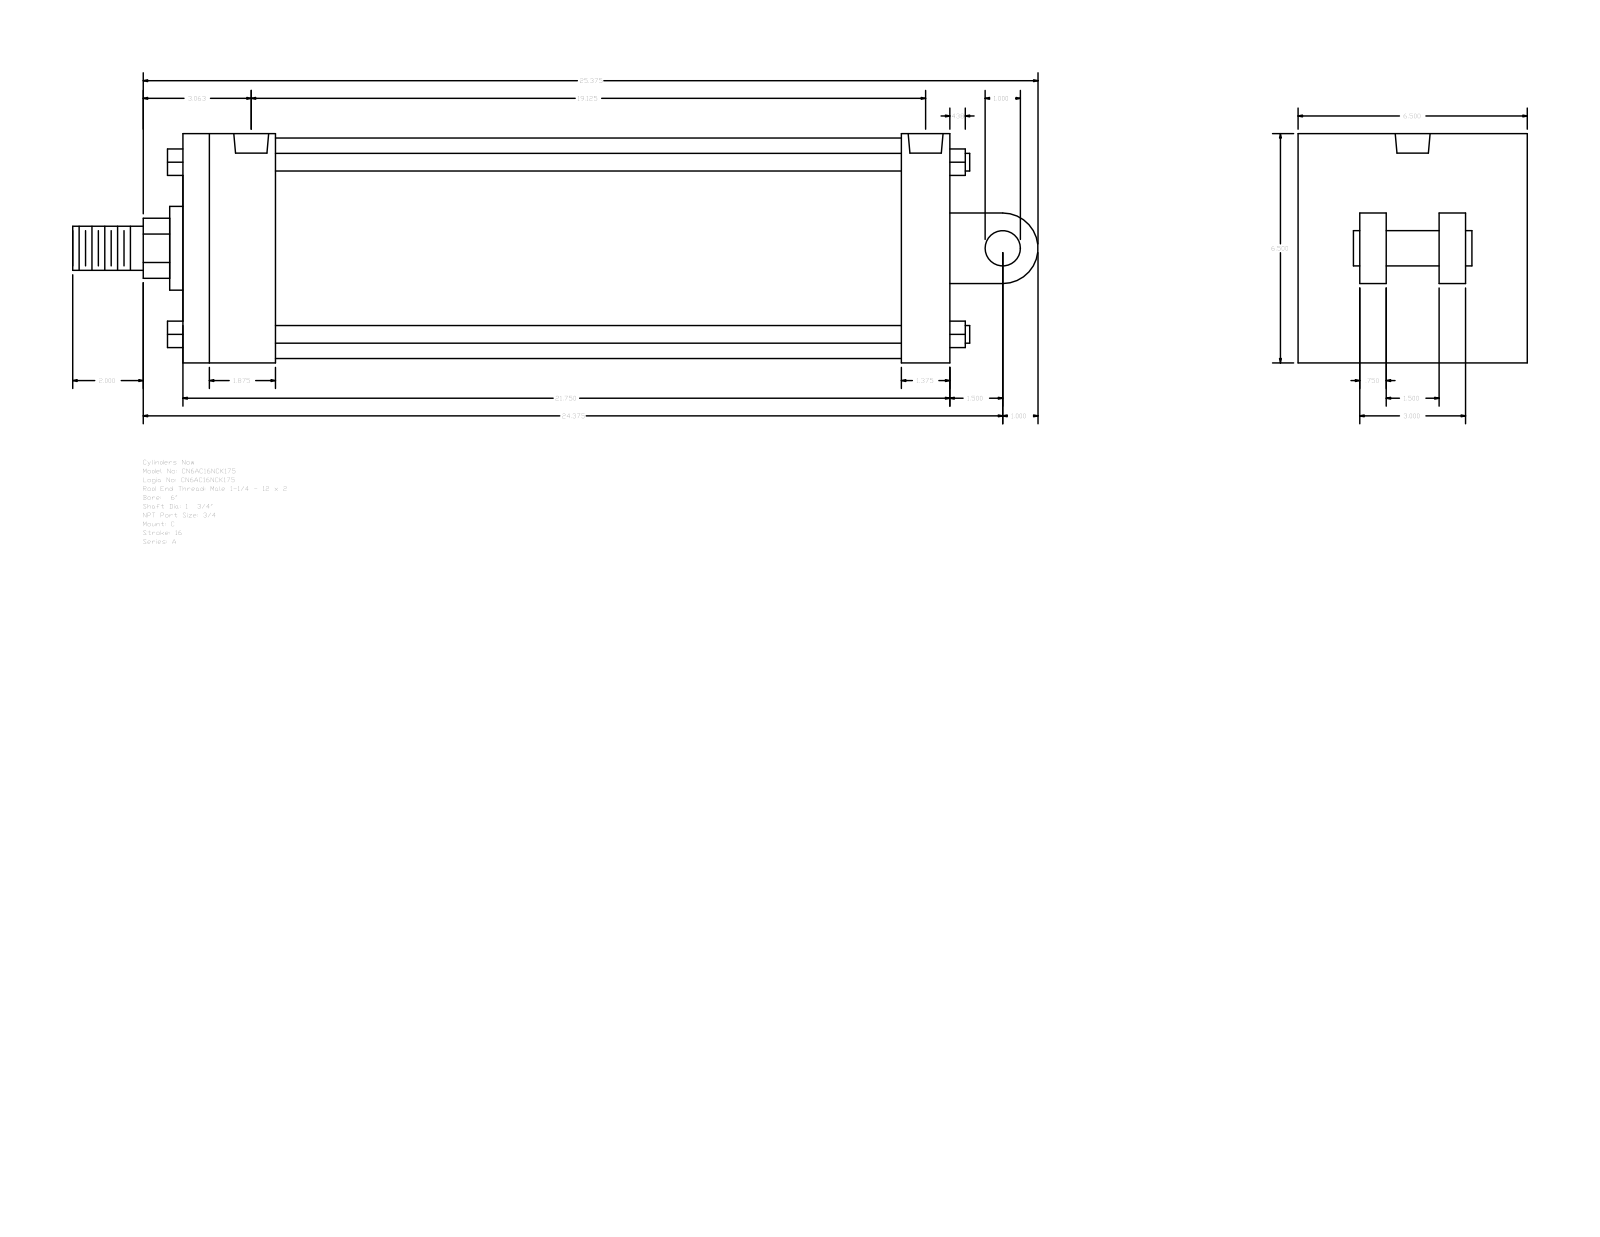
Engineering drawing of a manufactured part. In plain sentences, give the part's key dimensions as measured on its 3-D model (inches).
The part is named "A_C__0600_1.75". Its 3-D file was written by "GSSL Pune (CONFIG_CONTROL_DESIGN)". It is 0 solids with 135 faces: 102 planar, 33 cylindrical and 0 other. Overall it measures 27.375 by 6.5 by 6.5 inches. Round holes: 4 of diameter 0.594, 2 of diameter 0.989. Round bosses or shafts: 4 of diameter 0.5, 1 of diameter 6.25, 1 of diameter 2.375, 1 of diameter 1.75, 1 of diameter 1.25, 1 of diameter 1. Partial cylindrical surfaces (rounded edges, fillets, slot ends): 1 of radius 0.852, 1 of radius 1. The main face-to-face distances are 6.5, 21.75, 0.75, 2.25, 2.625, 19.125, 20.375, 17.75, 1.375, 2.5. The hole center spacings are 0.219, 18.687, 18.906, 19.125.
